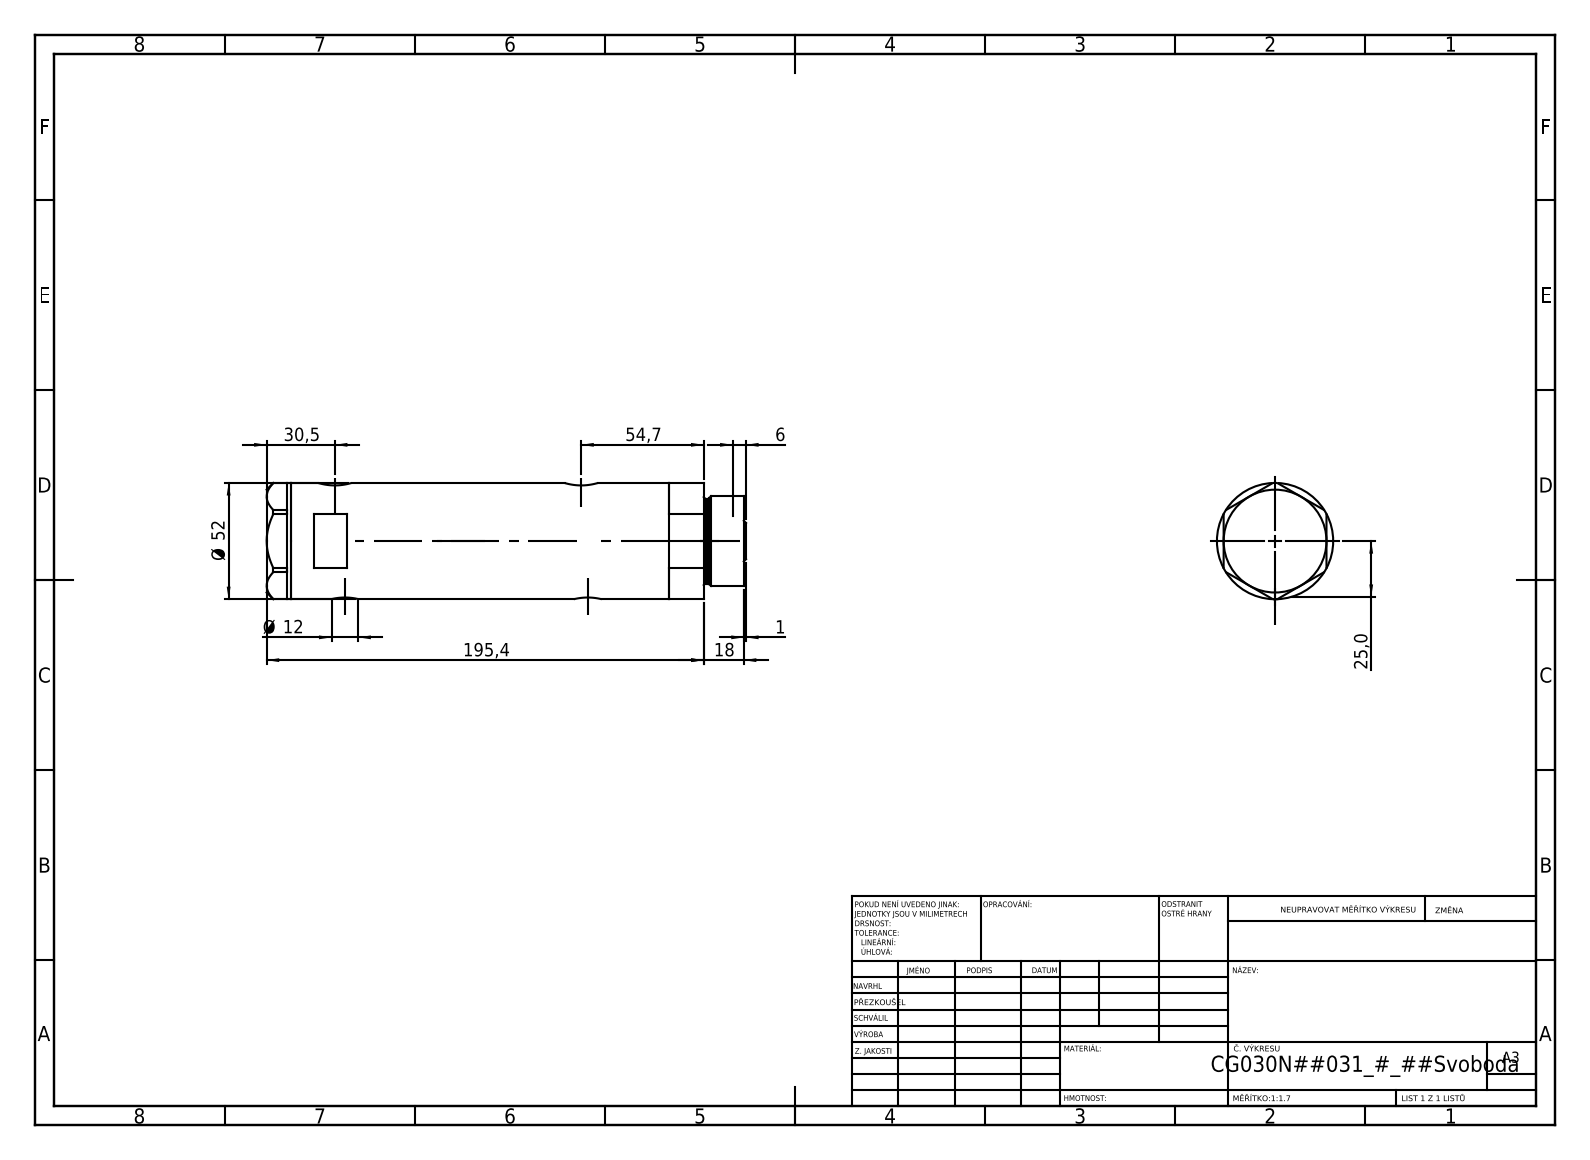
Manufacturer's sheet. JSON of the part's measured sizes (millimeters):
{"part_name": "V270CG_MIDDLE; V270CG_VC; V270CG_FRONT; V270CG_BACK", "step_written_by": "SolidWorks 2019 (CONFIG_CONTROL_DESIGN)", "units": "millimeters", "bodies": {"solids": 4, "faces": 140, "planar": 67, "cylindrical": 53, "other": 20}, "overall_size": [214.4, 52, 52], "volume_mm3": 411615, "surface_area_mm2": 89988, "round_holes": [[5, 2], [9.73, 2], [12.5, 2], [15, 2], [6.5, 1], [20, 1], [21.5, 1], [30, 1], [33, 1], [44, 1]], "round_bosses_or_shafts": [[12, 2], [52, 1], [40, 1], [38, 1], [19, 1]], "face_to_face_distances": [132.5, 23.8, 108.7, 11, 34.8, 143.5, 46, 179.9, 168.9, 145.1], "hole_center_spacings": [2.9, 4.5, 105.7, 108.6, 110.2, 113.1]}
